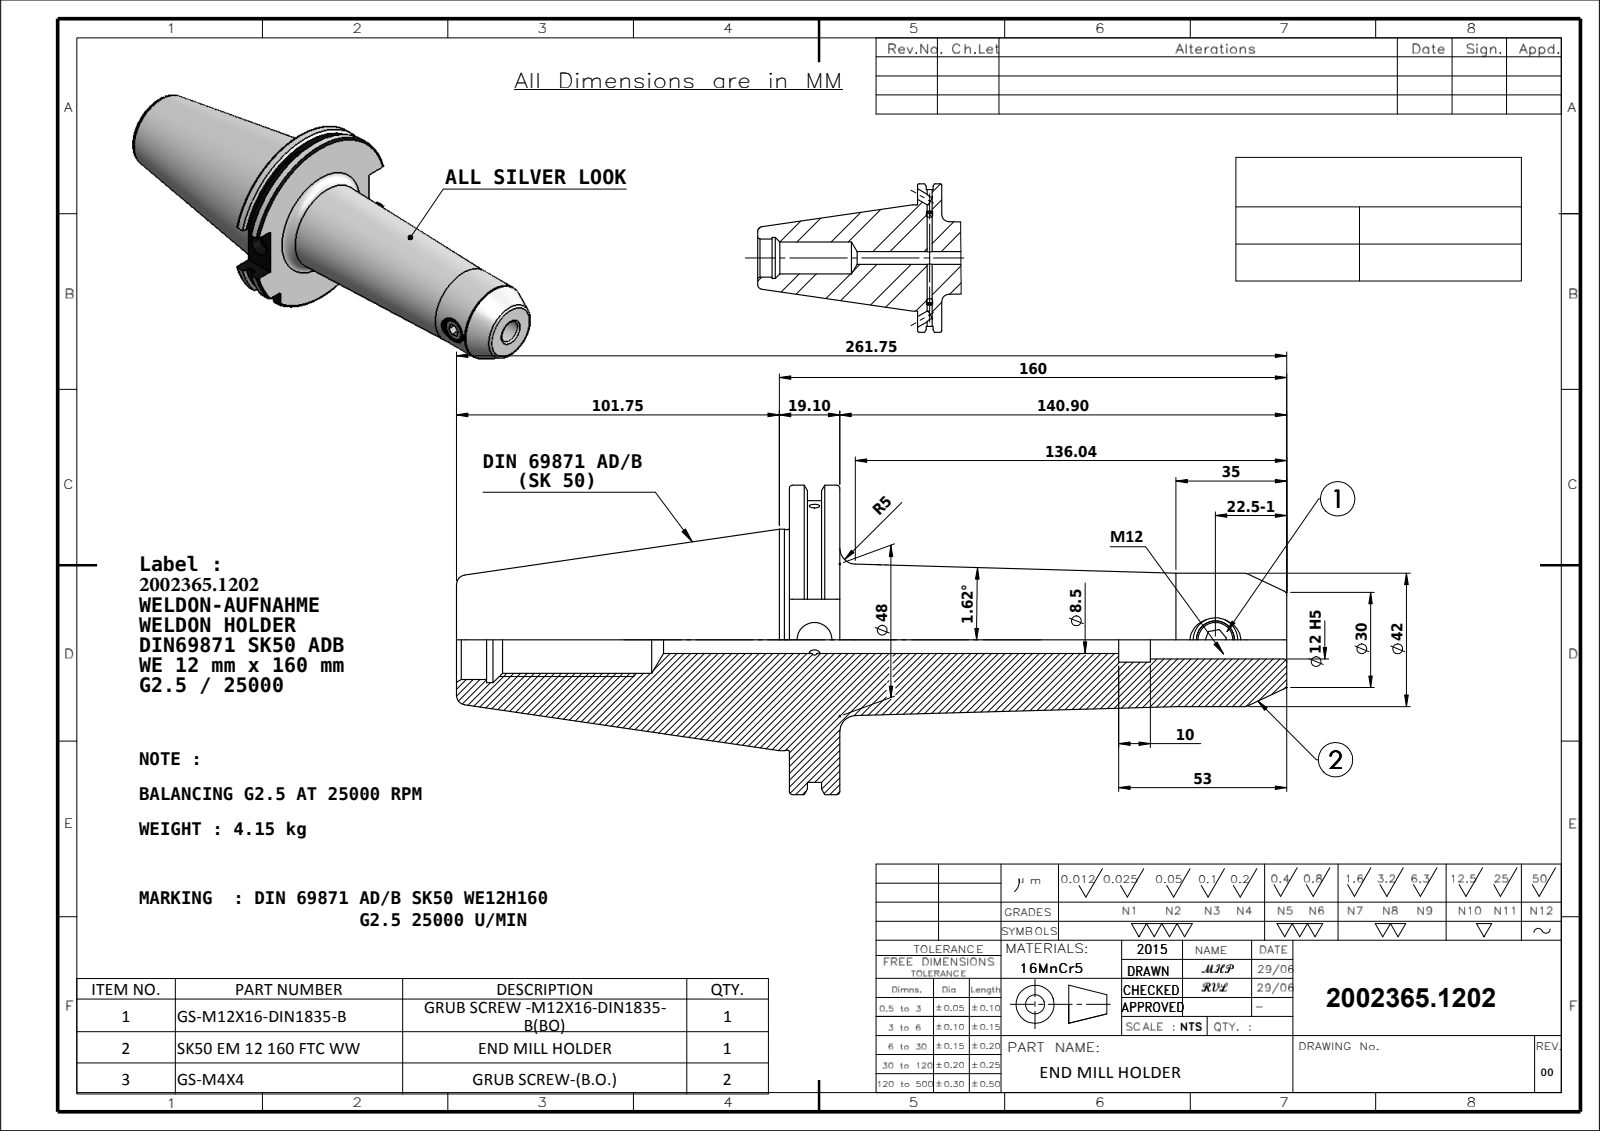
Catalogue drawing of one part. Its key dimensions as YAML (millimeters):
part_name: "SK50 EM 12 160 FTC WW; M4X4_DIN 913 - M4 x 4-N; M12X16 SPL; 91506-WE712160"
step_written_by: "SolidWorks 2009 (CONFIG_CONTROL_DESIGN)"
units: millimeters
bodies: {solids: 4, faces: 172, planar: 53, cylindrical: 55, other: 64}
overall_size: [261.75, 97.5, 94.05]
volume: 536019
surface_area: 67115
round_holes:
  - {diameter: 6, count: 2}
  - {diameter: 14, count: 2}
  - {diameter: 3.3, count: 1}
  - {diameter: 8.5, count: 1}
  - {diameter: 10.2, count: 1}
  - {diameter: 11, count: 1}
  - {diameter: 12, count: 1}
  - {diameter: 21, count: 1}
  - {diameter: 25, count: 1}
  - {diameter: 27, count: 1}
round_bosses_or_shafts:
  - {diameter: 4, count: 2}
  - {diameter: 69.85, count: 1}
  - {diameter: 69.45, count: 1}
  - {diameter: 42, count: 1}
  - {diameter: 12, count: 1}
partial_cylinders:
  - {radius: 44.9, count: 1}
  - {radius: 48.75, count: 1}
face_to_face_distances: [15.9, 5.66, 10.24, 10.15, 4.49, 5.75, 156.8, 151.14, 146.65, 140.9]
hole_center_spacings: [126.4]
